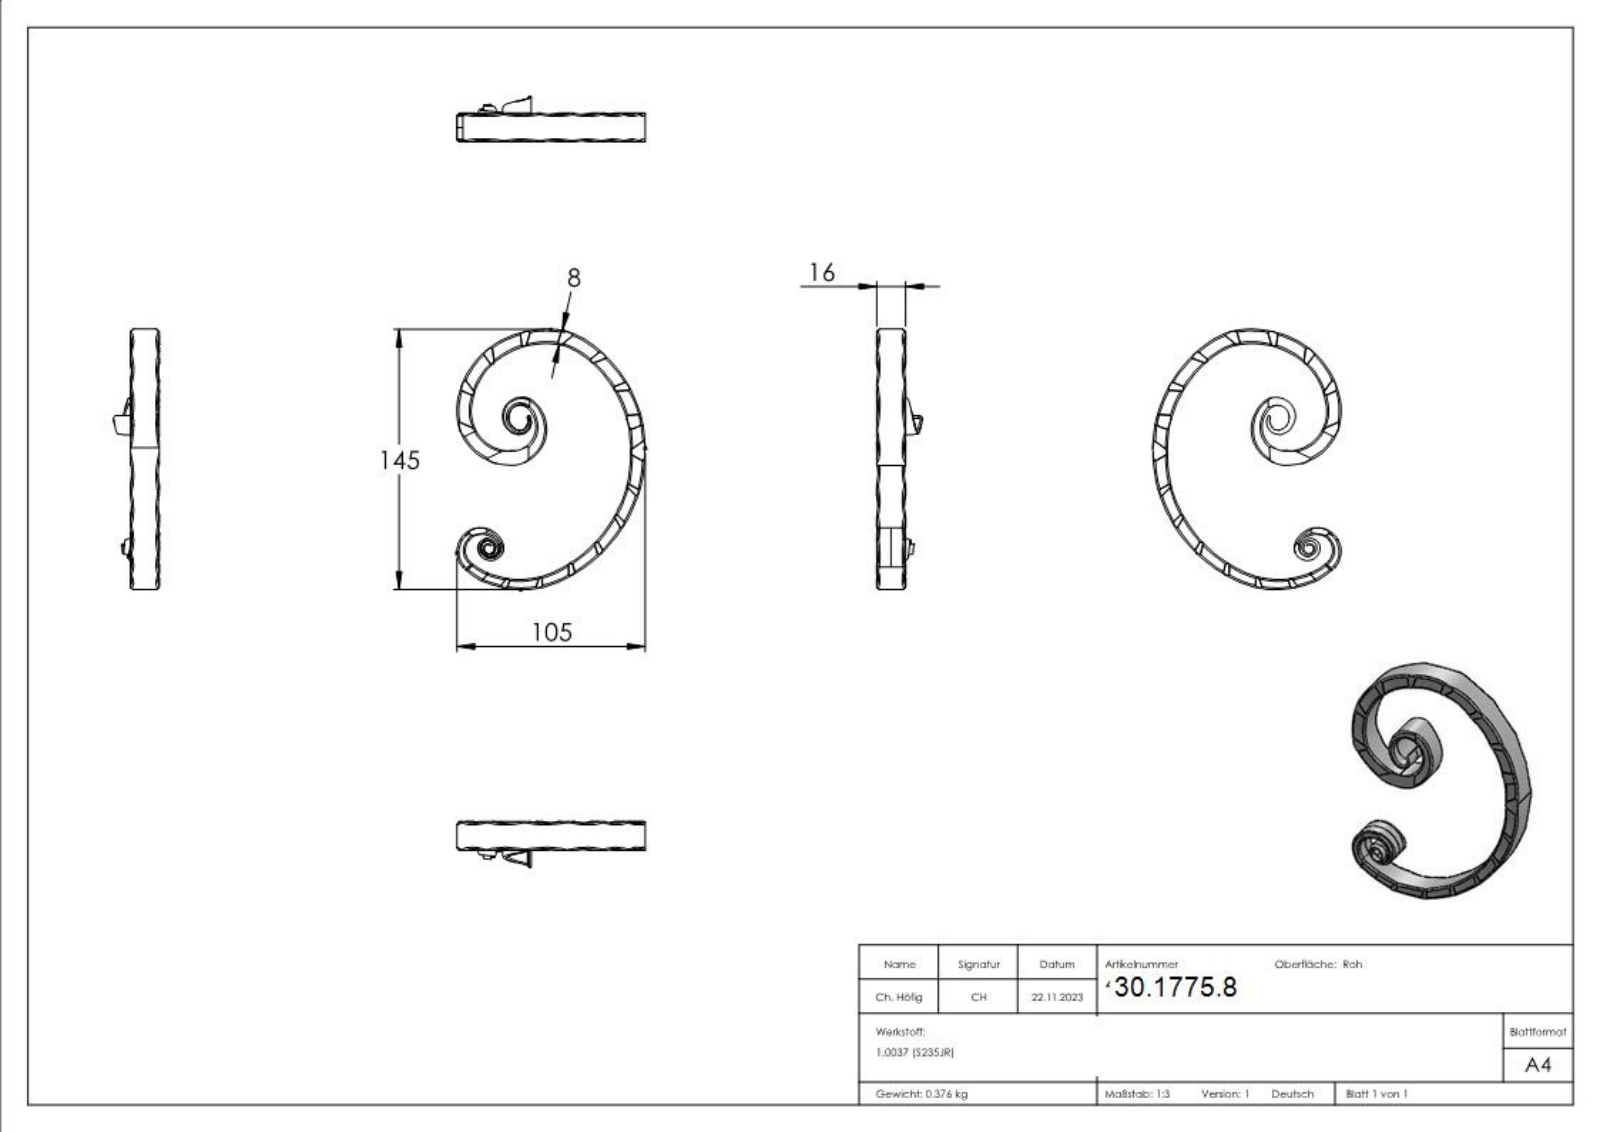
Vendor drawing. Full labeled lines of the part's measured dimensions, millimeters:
Part name (STEP PRODUCT): 4515
STEP written by: SolidWorks 2018 (CONFIG_CONTROL_DESIGN)
Units: millimetres
Bodies: 1 solid, 289 faces (50 planar, 91 cylindrical, 148 other)
Overall size (bounding box): 145.06 × 104.98 × 26.16
Volume: 48 222 mm³ · Surface area: 22 145 mm²
Partial cylindrical surfaces — rounded edges, fillets, slot ends (radius × count): R1 ×65, R37.88 ×22, R17.61 ×2
Main face-to-face distances: 16
